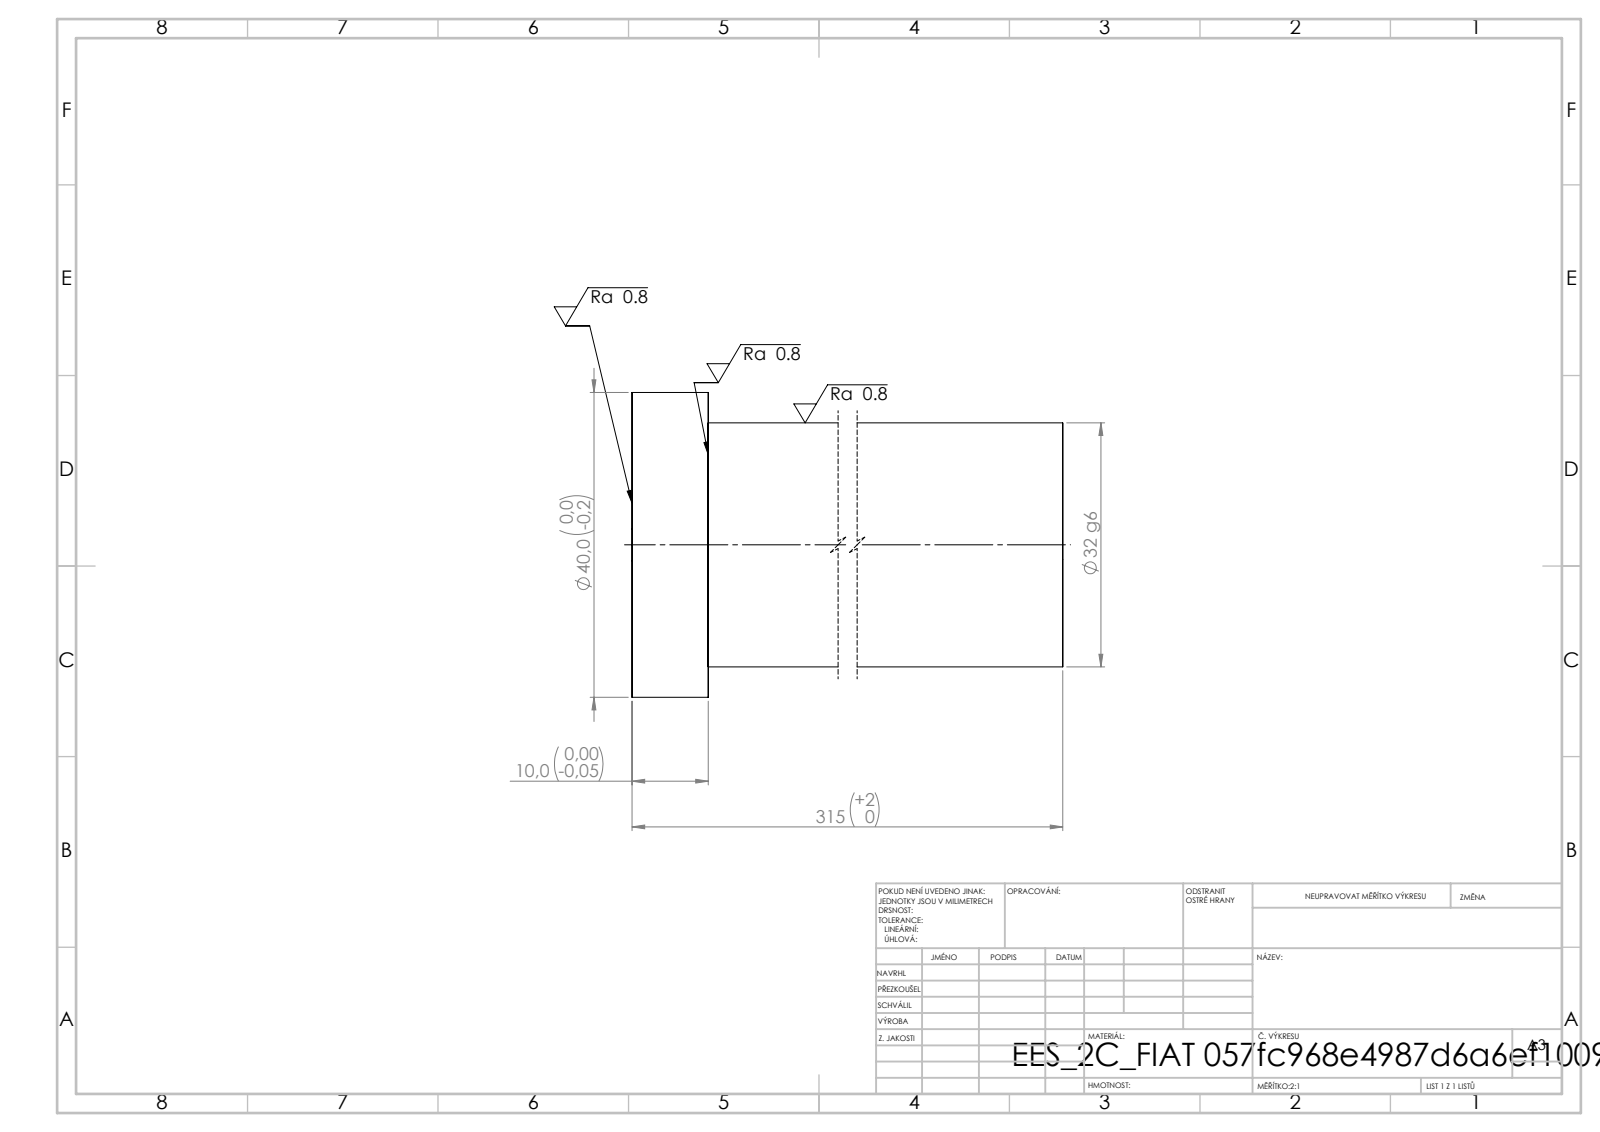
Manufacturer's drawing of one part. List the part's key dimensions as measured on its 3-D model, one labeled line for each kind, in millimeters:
STEP written by: SolidWorks 2019 (CONFIG_CONTROL_DESIGN)
Units: millimetres
Bodies: 1 solid, 7 faces (3 planar, 4 cylindrical, 0 other)
Overall size (bounding box): 315 × 40 × 40
Volume: 257 862 mm³ · Surface area: 34 432 mm²
Round bosses / shafts (diameter × count): ⌀40 ×1, ⌀32 ×1
Main face-to-face distances: 315, 10, 305
